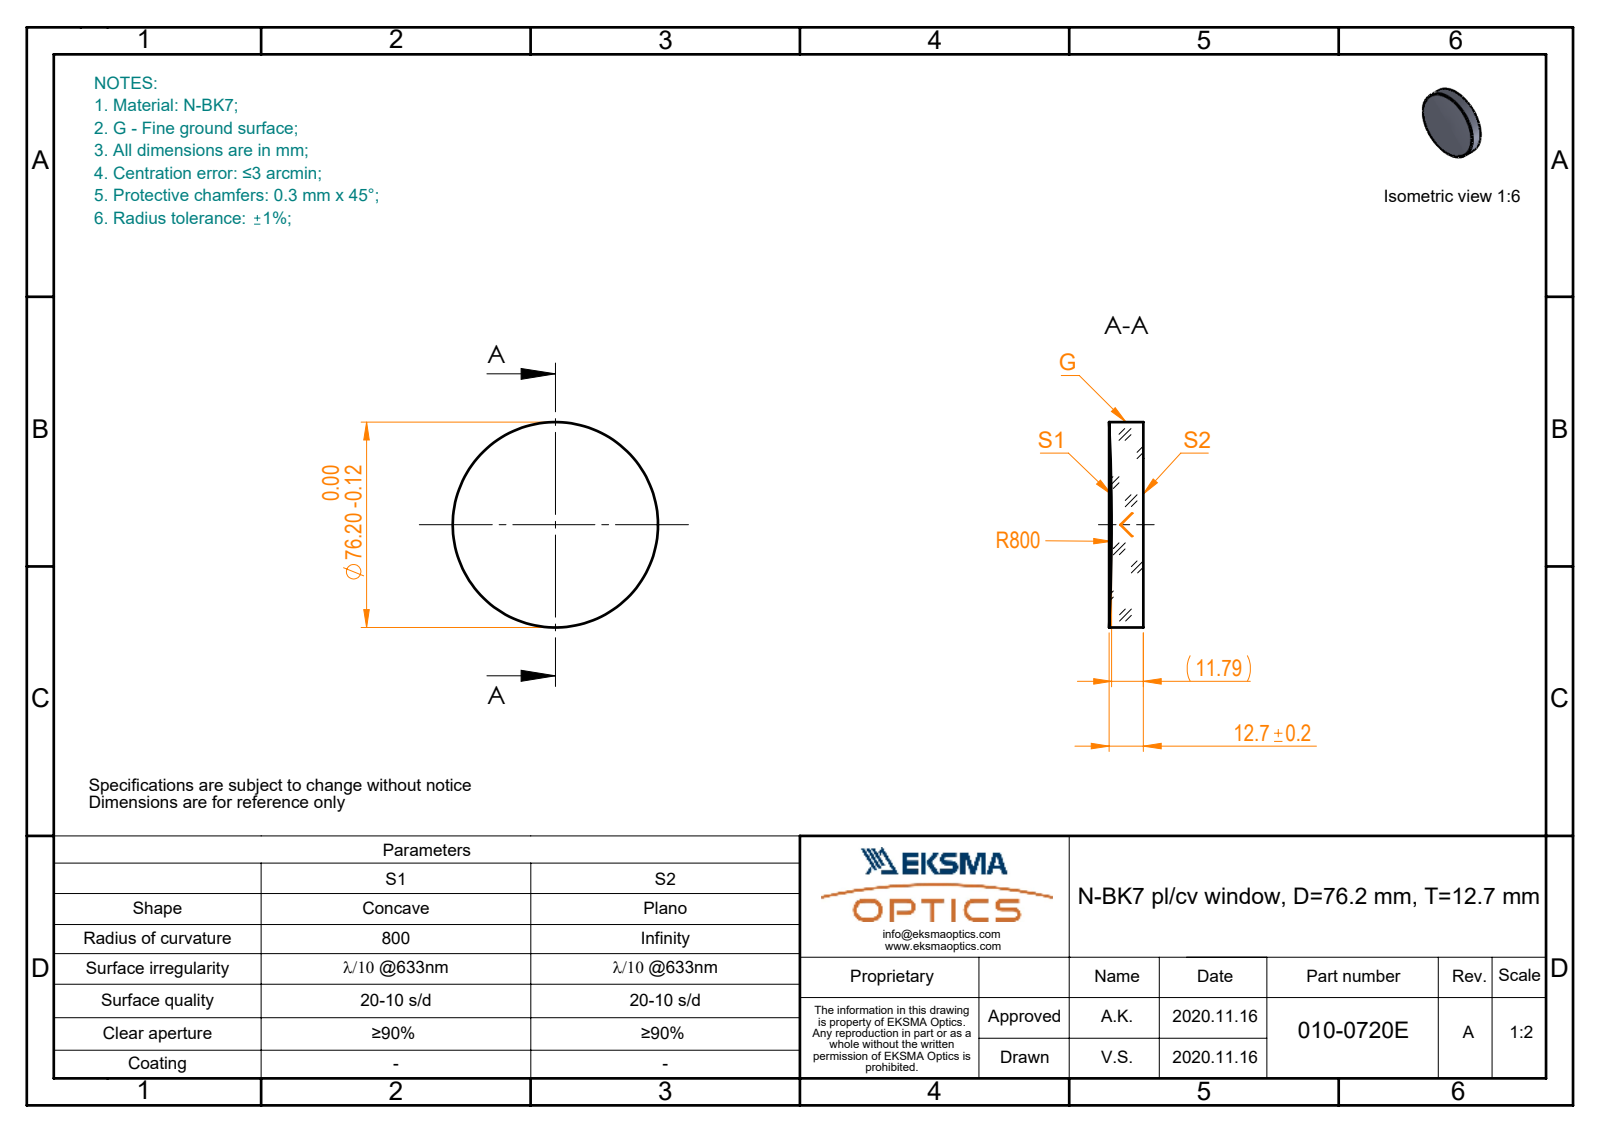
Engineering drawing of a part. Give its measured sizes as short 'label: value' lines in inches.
name: 010-0720E_N-BK7_PCV_window
written by: SolidWorks 2019 (CONFIG_CONTROL_DESIGN)
unit: in
bodies: 1 solid, 5 faces (1 planar, 2 cylindrical, 2 other)
size: 3 × 3 × 0.5
volume: 3.408 in³; area: 18.85 in²
bosses: 1× ⌀3
